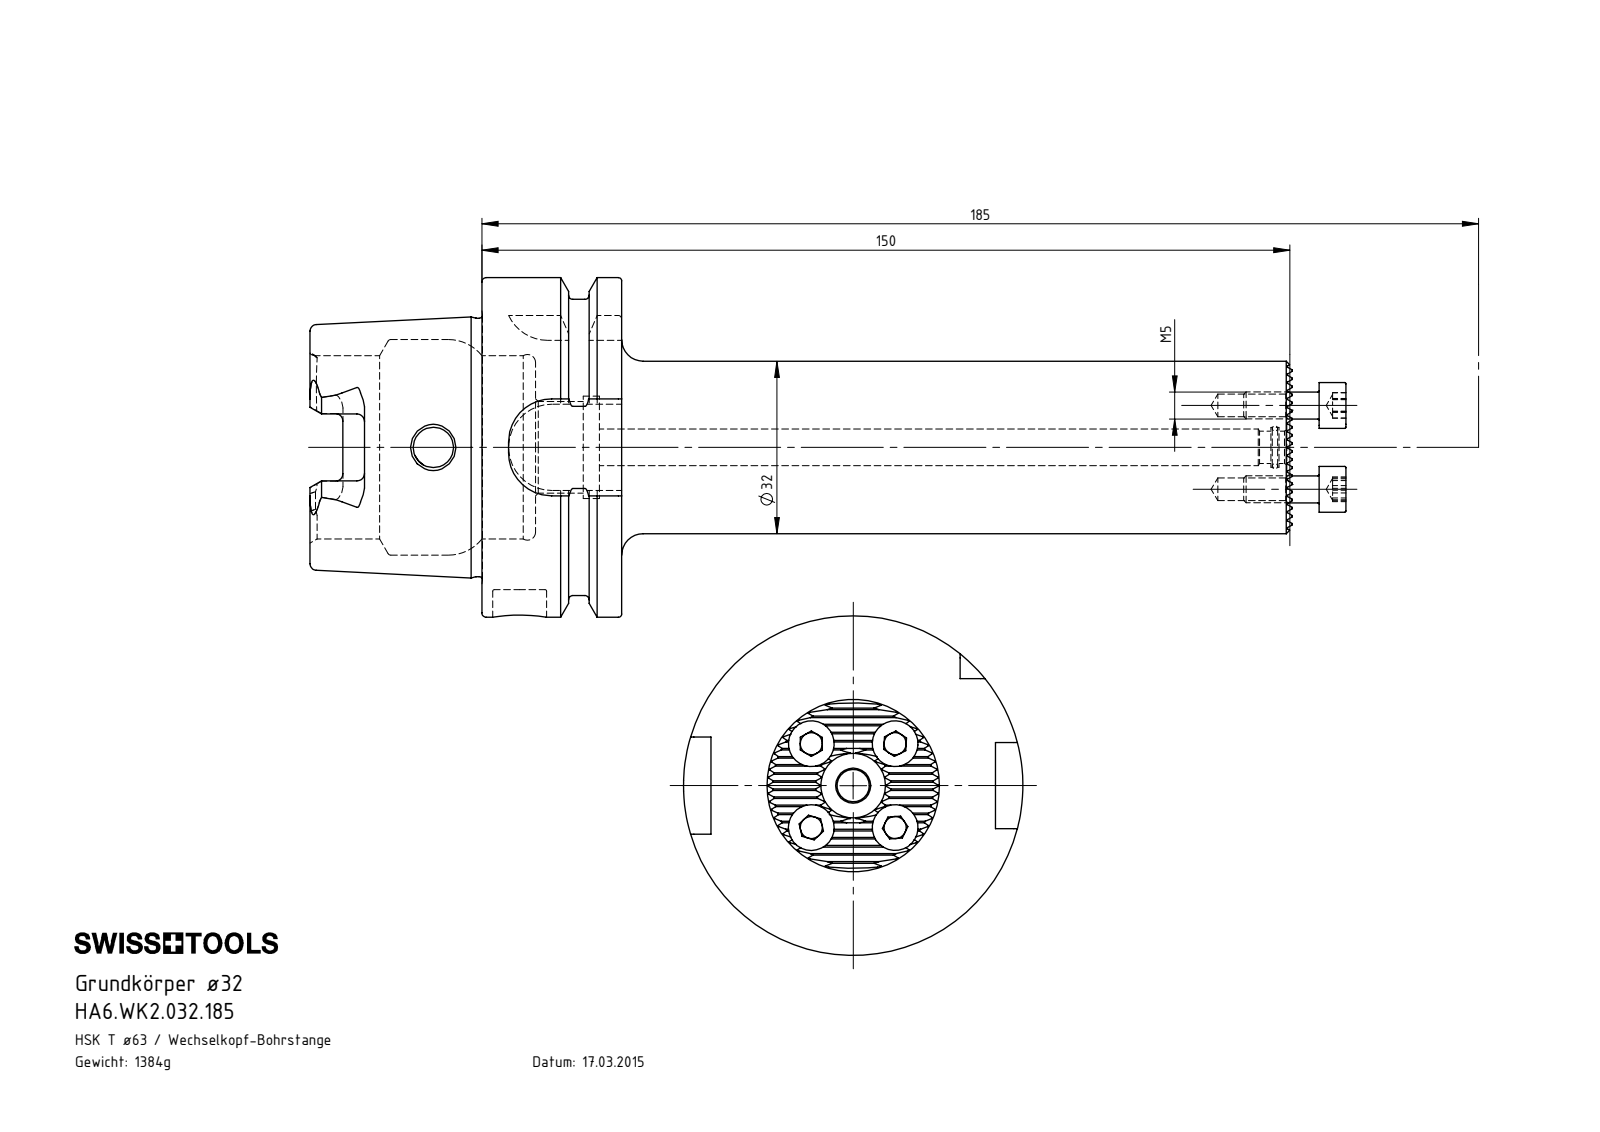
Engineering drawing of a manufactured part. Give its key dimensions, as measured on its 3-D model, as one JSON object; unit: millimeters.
{"part_name": "DIN 3771 - 6x1; WK1-ER1.016.112_A_Fertigbearbeitung; ISO 4762 - M5 x 14; WK1-ER1.016.002_A_Fertigbearbeitung (+3 more)", "step_written_by": "SolidWorks 2017 (AUTOMOTIVE_DESIGN)", "units": "millimeters", "bodies": {"solids": 8, "faces": 498, "planar": 236, "cylindrical": 125, "other": 137}, "overall_size": [192.3, 63, 63], "volume_mm3": 179925, "surface_area_mm2": 54477, "round_holes": [[4.2, 4], [3, 1], [6, 1], [7.4, 1], [7.5, 1], [10, 1], [16.5, 1], [17, 1], [19, 1], [26.5, 1], [29, 1], [34, 1]], "round_bosses_or_shafts": [[8.5, 3], [5, 3], [63, 1], [54.95, 1], [47.94, 1], [32, 1], [28, 1], [16, 1]], "partial_cylinders_radius": [[0.12, 21], [1.4, 6], [2.88, 4], [8, 4]], "face_to_face_distances": [1, 25.95, 24.95, 1.3, 2.6, 16, 9.95, 15, 3.9, 137.6], "hole_center_spacings": [11, 15.56, 22.01]}
